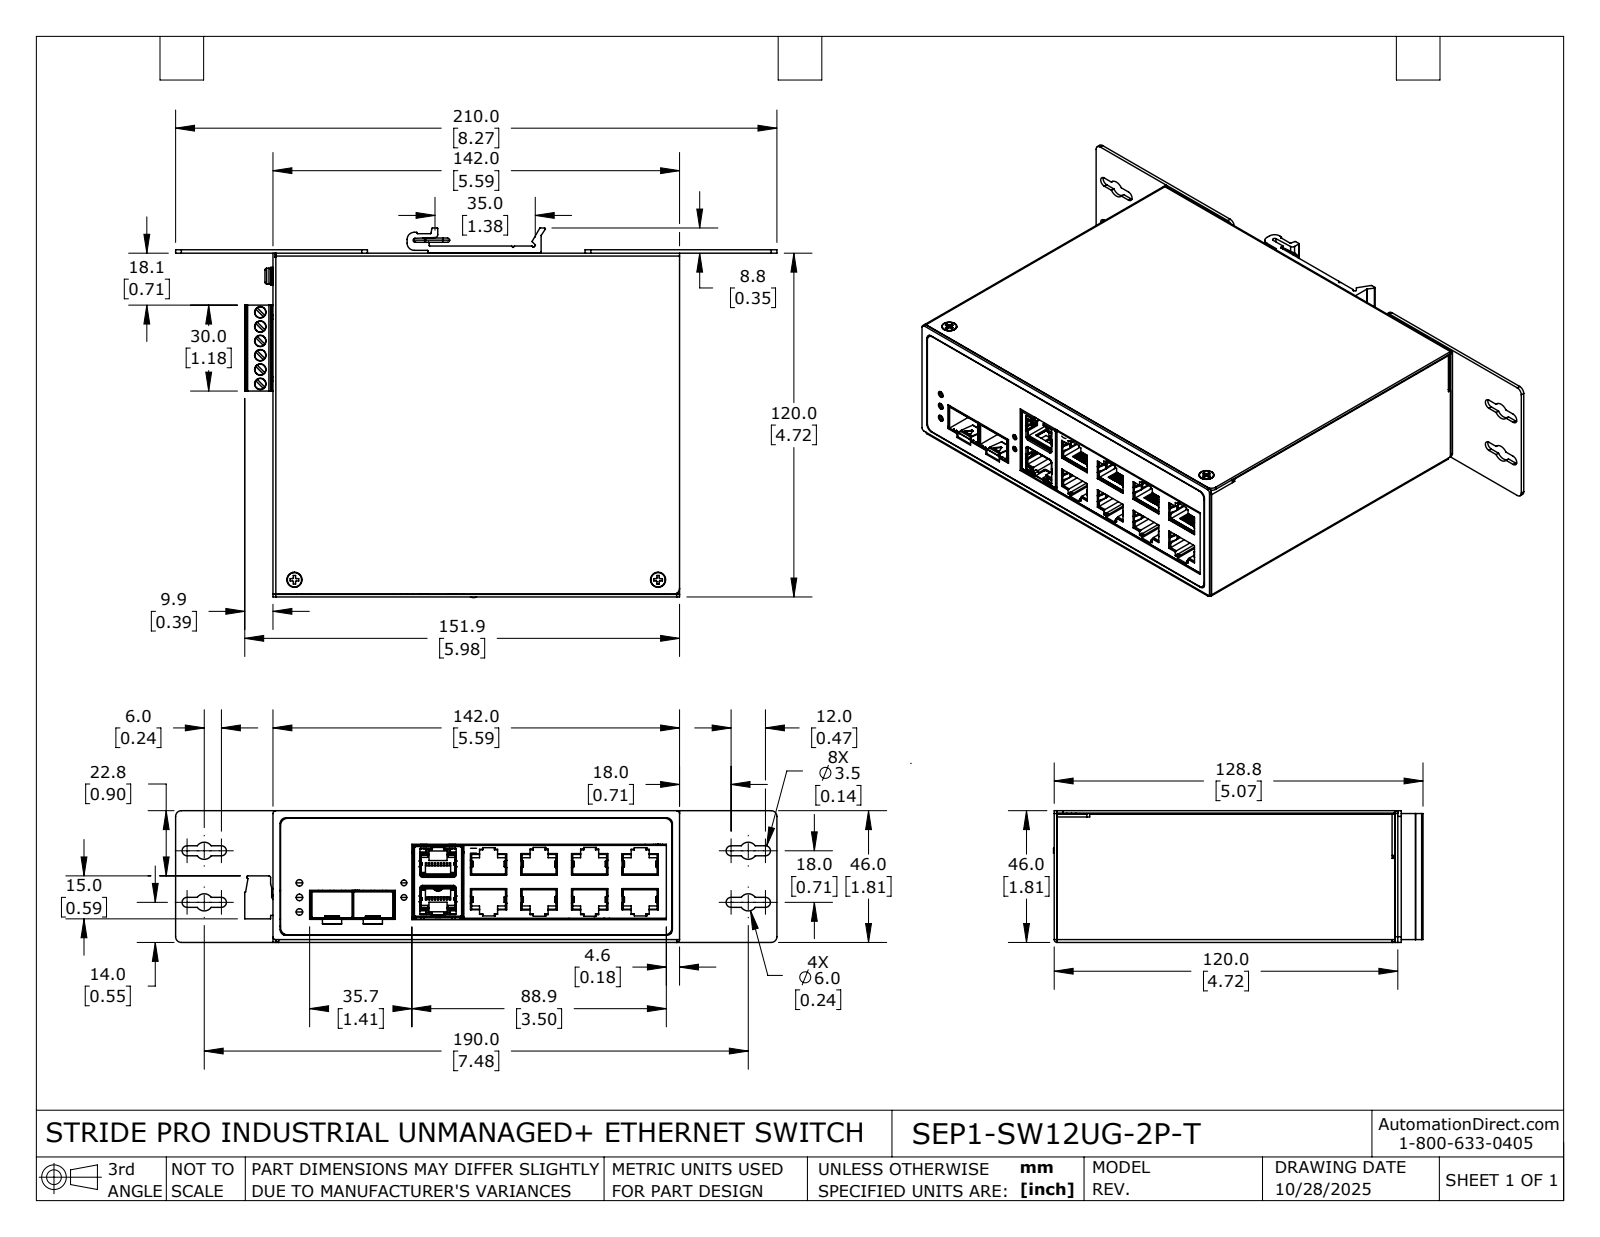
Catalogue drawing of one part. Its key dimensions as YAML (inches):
part_name: "SEP1-SW12UG-2P-T"
step_written_by: "SolidWorks 2024 (AUTOMOTIVE_DESIGN)"
units: inches
bodies: {solids: 46, faces: 6527, planar: 4142, cylindrical: 1836, other: 549}
overall_size: [5.978, 5.081, 1.811]
volume: 8.538
surface_area: 303.4
round_holes:
  - {diameter: 0.157, count: 19}
  - {diameter: 0.209, count: 7}
  - {diameter: 0.055, count: 6}
  - {diameter: 0.11, count: 5}
  - {diameter: 0.126, count: 5}
  - {diameter: 0.097, count: 4}
  - {diameter: 0.079, count: 3}
  - {diameter: 0.091, count: 3}
  - {diameter: 0.039, count: 2}
  - {diameter: 0.096, count: 2}
  - {diameter: 0.096, count: 2}
  - {diameter: 0.024, count: 1}
round_bosses_or_shafts:
  - {diameter: 0.118, count: 16}
  - {diameter: 0.02, count: 12}
  - {diameter: 0.197, count: 10}
  - {diameter: 0.149, count: 6}
  - {diameter: 0.059, count: 6}
  - {diameter: 0.165, count: 4}
  - {diameter: 0.157, count: 4}
  - {diameter: 0.149, count: 4}
partial_cylinders:
  - {radius: 0.008, count: 210}
  - {radius: 0.004, count: 162}
  - {radius: 0.01, count: 99}
  - {radius: 0.008, count: 80}
  - {radius: 0.02, count: 72}
  - {radius: 0.006, count: 57}
  - {radius: 0.016, count: 48}
  - {radius: 0.039, count: 36}
face_to_face_distances: [0.035, 1.776, 1.74, 0.283, 1.457, 1.492, 0.22, 0.063, 1.52, 1.555]
hole_center_spacings: [0.197, 0.394, 0.591, 0.787, 0.2, 1.451, 0.037, 0.419]
